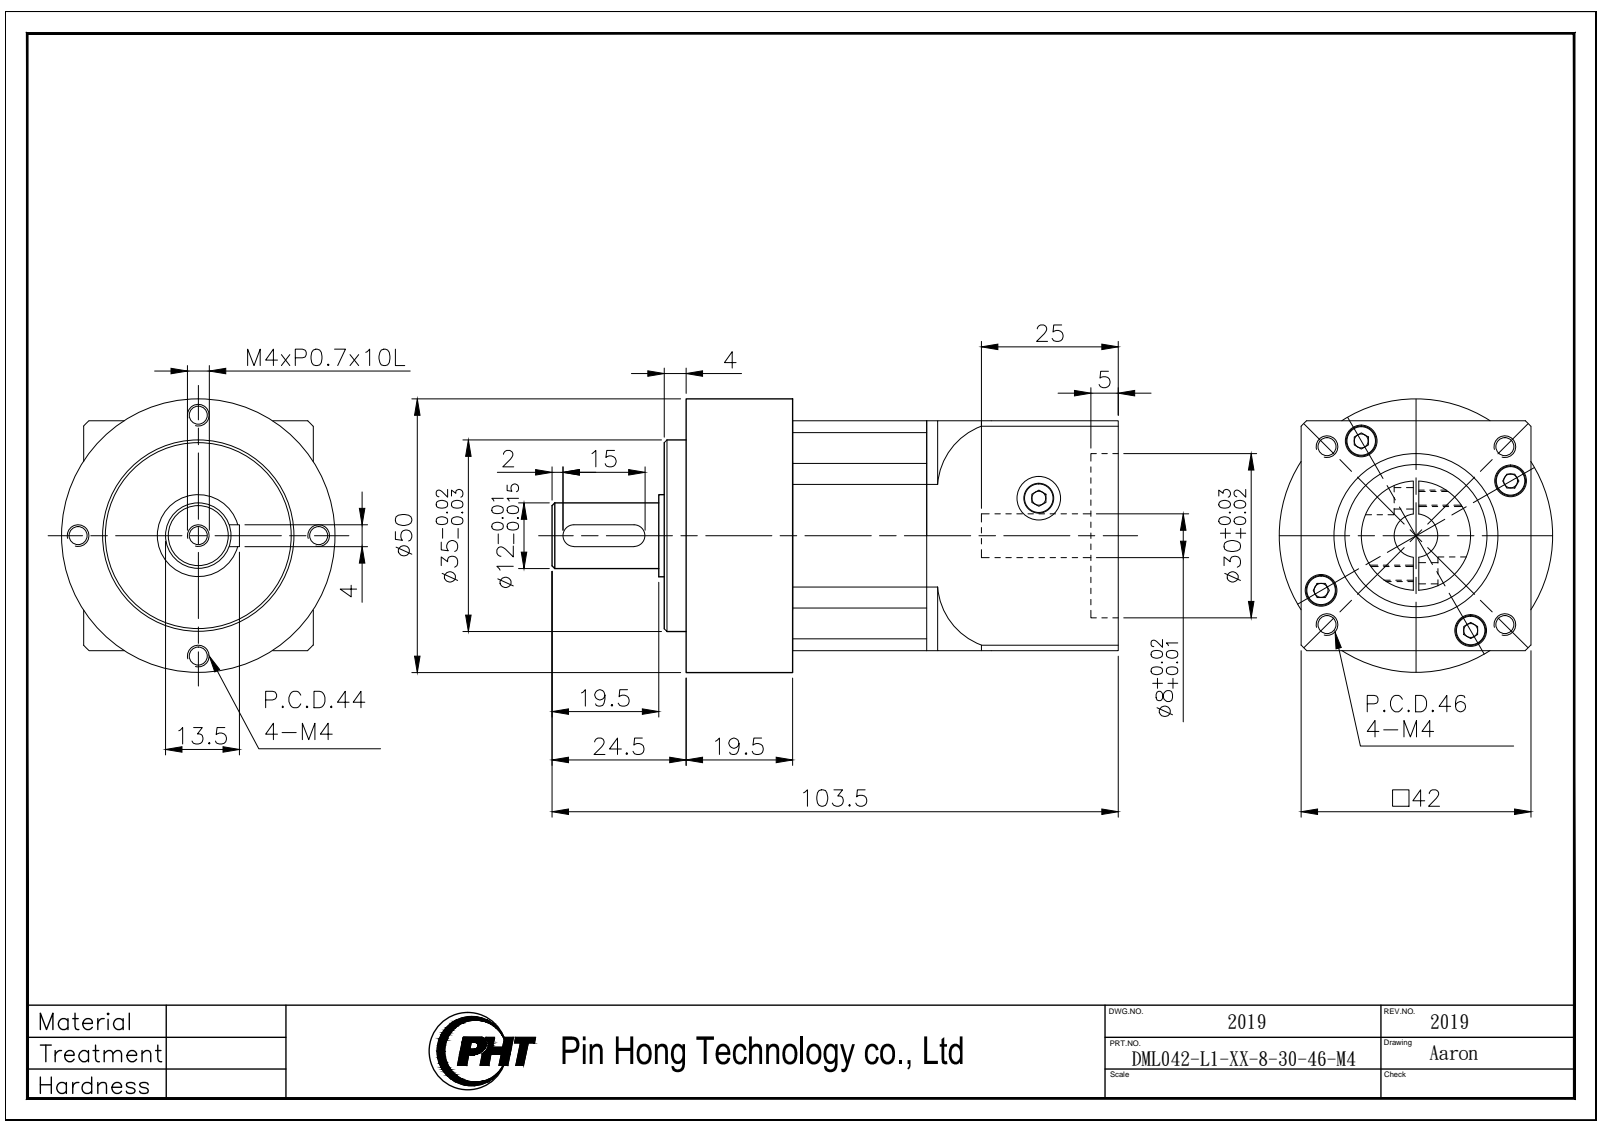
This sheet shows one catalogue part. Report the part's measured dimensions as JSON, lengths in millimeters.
{"part_name": "DML042-L1-XX-8-30-46-M4_2019", "step_written_by": "SolidWorks 2016 (AUTOMOTIVE_DESIGN)", "units": "millimeters", "bodies": {"solids": 3, "faces": 189, "planar": 68, "cylindrical": 89, "other": 32}, "overall_size": [103.5, 50, 50], "volume_mm3": 127935, "surface_area_mm2": 31883, "round_holes": [[3.3, 13], [5.8, 4], [8, 3], [26, 1], [30, 1]], "round_bosses_or_shafts": [[5.5, 4], [50, 1], [35, 1], [20, 1], [15, 1], [12, 1]], "partial_cylinders_radius": [[4, 4], [2, 2], [23, 1], [29, 1]], "face_to_face_distances": [42, 24.5, 44, 19.5, 79, 35, 59.5, 4, 83, 48], "hole_center_spacings": [17.24, 41.57, 6.35, 11.04, 20, 21.07, 22, 23]}
